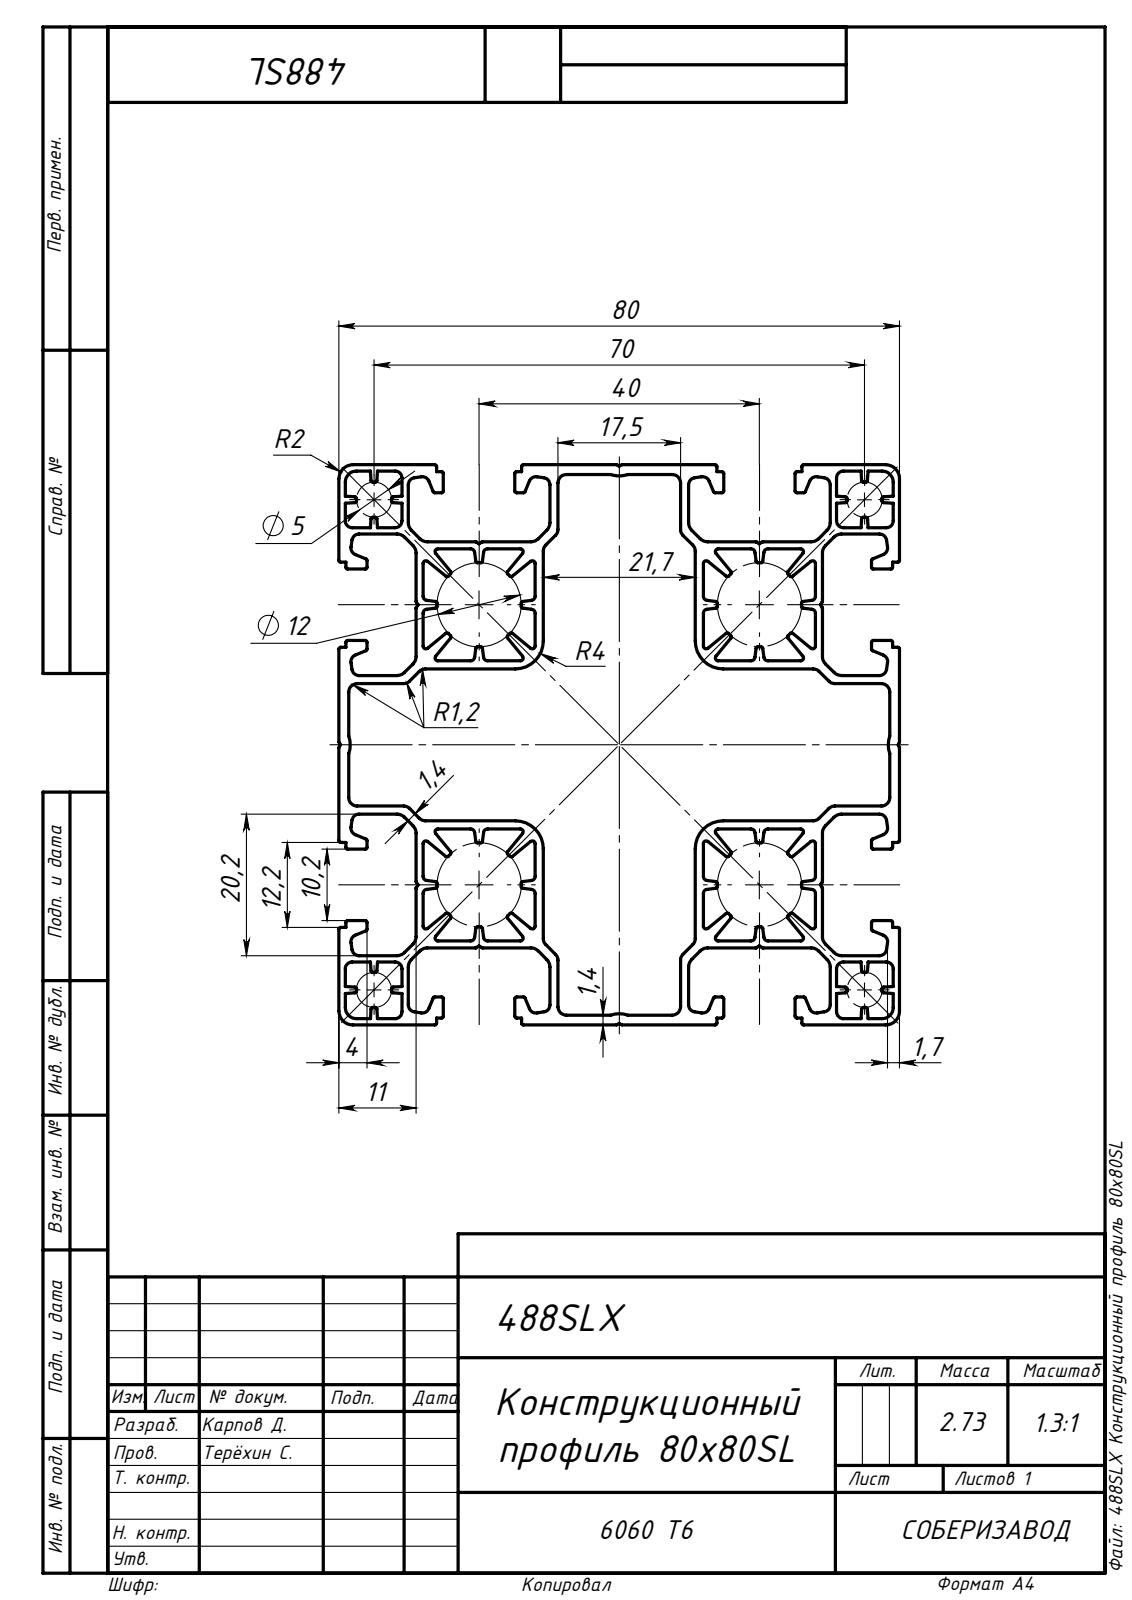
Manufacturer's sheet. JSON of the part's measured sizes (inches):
{"step_written_by": "SolidWorks 2019 (AUTOMOTIVE_DESIGN)", "units": "inches", "bodies": {"solids": 1, "faces": 846, "planar": 426, "cylindrical": 420, "other": 0}, "overall_size": [39.37, 3.15, 3.15], "volume_in3": 61.82, "surface_area_in2": 2361, "partial_cylinders_radius": [[0.01, 176], [0.039, 44], [0.016, 32], [0.024, 32], [0.059, 32], [0.047, 24], [0.157, 8], [0.063, 4]], "face_to_face_distances": [0.083, 0.046, 1.529, 1.575, 0.433, 2.717, 1.148, 2.002, 0.715, 1.569]}
